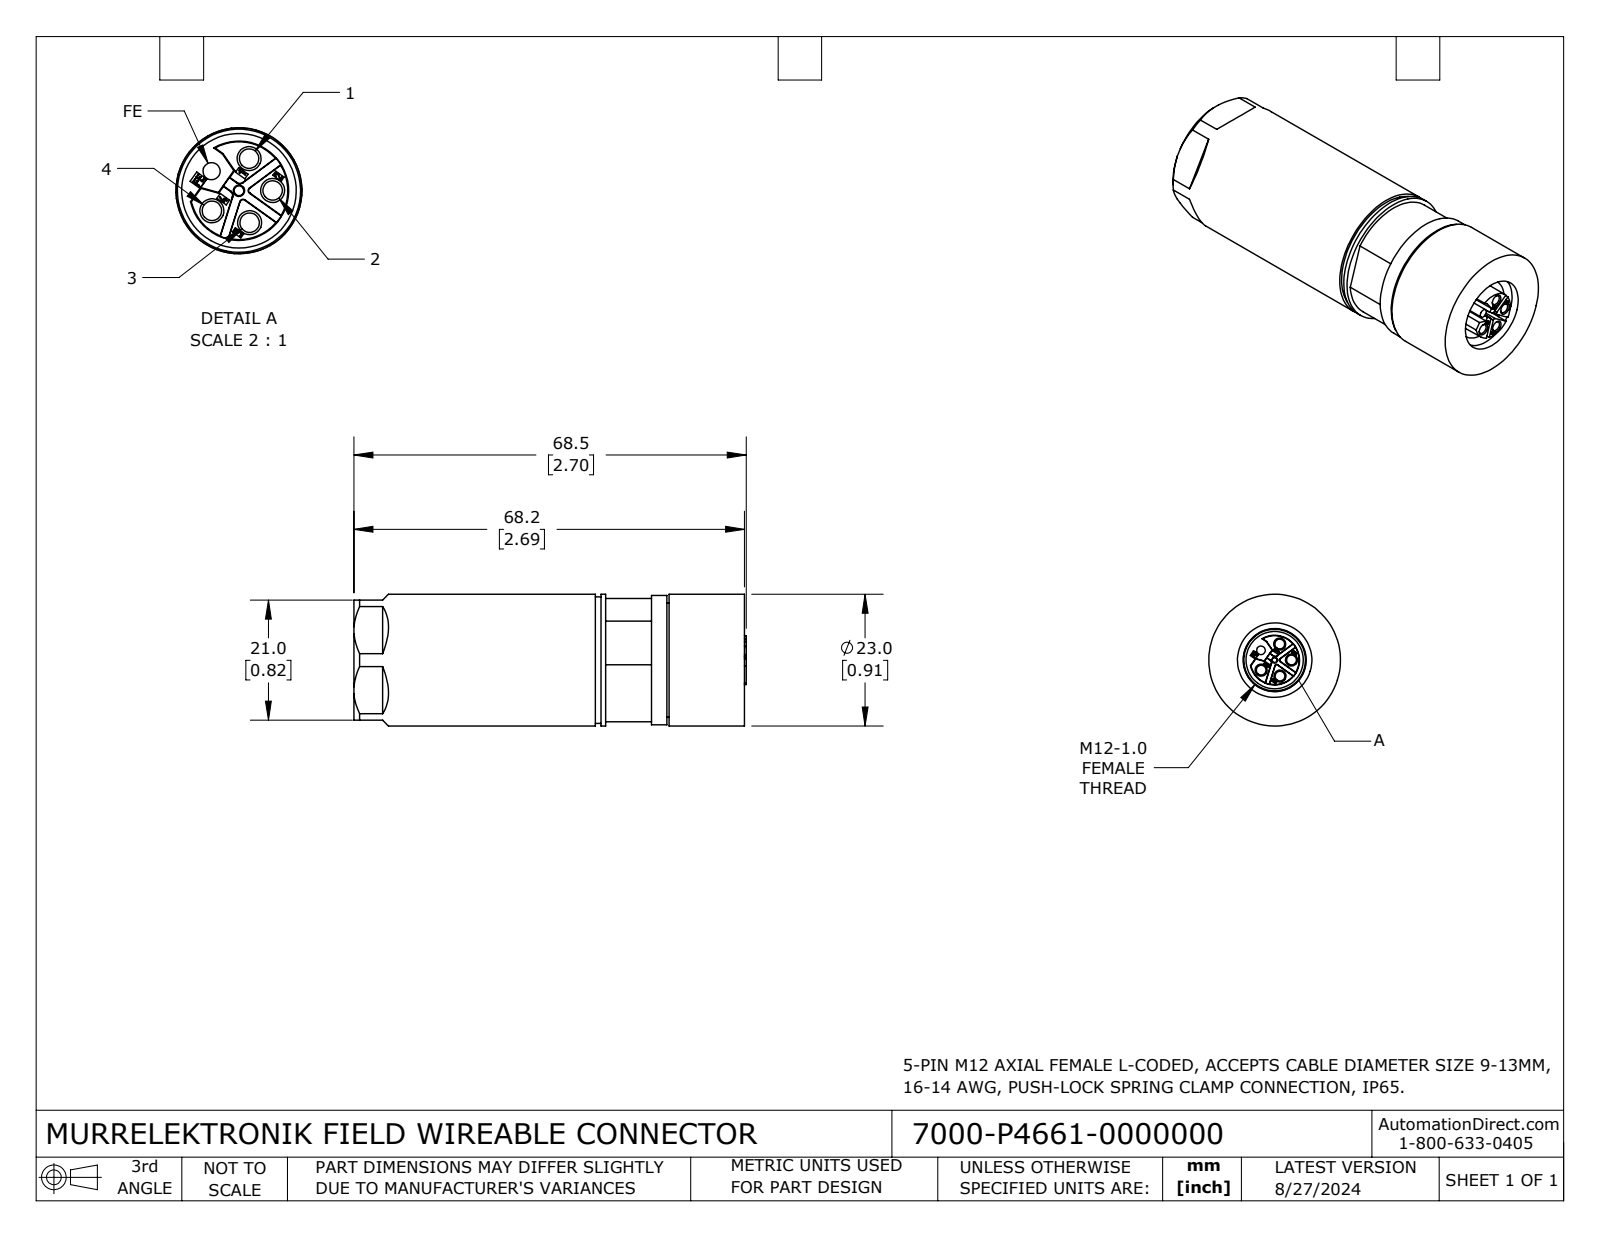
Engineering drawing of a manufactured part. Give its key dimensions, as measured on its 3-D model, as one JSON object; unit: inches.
{"part_name": "7000-P4661-0000000", "step_written_by": "SolidWorks 2023 (CONFIG_CONTROL_DESIGN)", "units": "inches", "bodies": {"solids": 2, "faces": 262, "planar": 134, "cylindrical": 96, "other": 32}, "overall_size": [2.697, 0.906, 0.906], "volume_in3": 1.555, "surface_area_in2": 12.87, "round_holes": [[0.067, 4], [0.327, 1], [0.423, 1], [0.433, 1], [0.512, 1], [0.701, 1]], "round_bosses_or_shafts": [[0.906, 1], [0.89, 1], [0.87, 1], [0.787, 1], [0.394, 1], [0.059, 1]], "partial_cylinders_radius": [[0.004, 4], [0.007, 3], [0.007, 2], [0.008, 2], [0.372, 1], [0.423, 1]], "face_to_face_distances": [0.612, 2.685, 2.073, 0.246, 0.518, 0.094, 2.167, 2.63, 2.112, 2.018], "hole_center_spacings": [0.116, 0.136, 0.22, 0.136, 0.22]}
